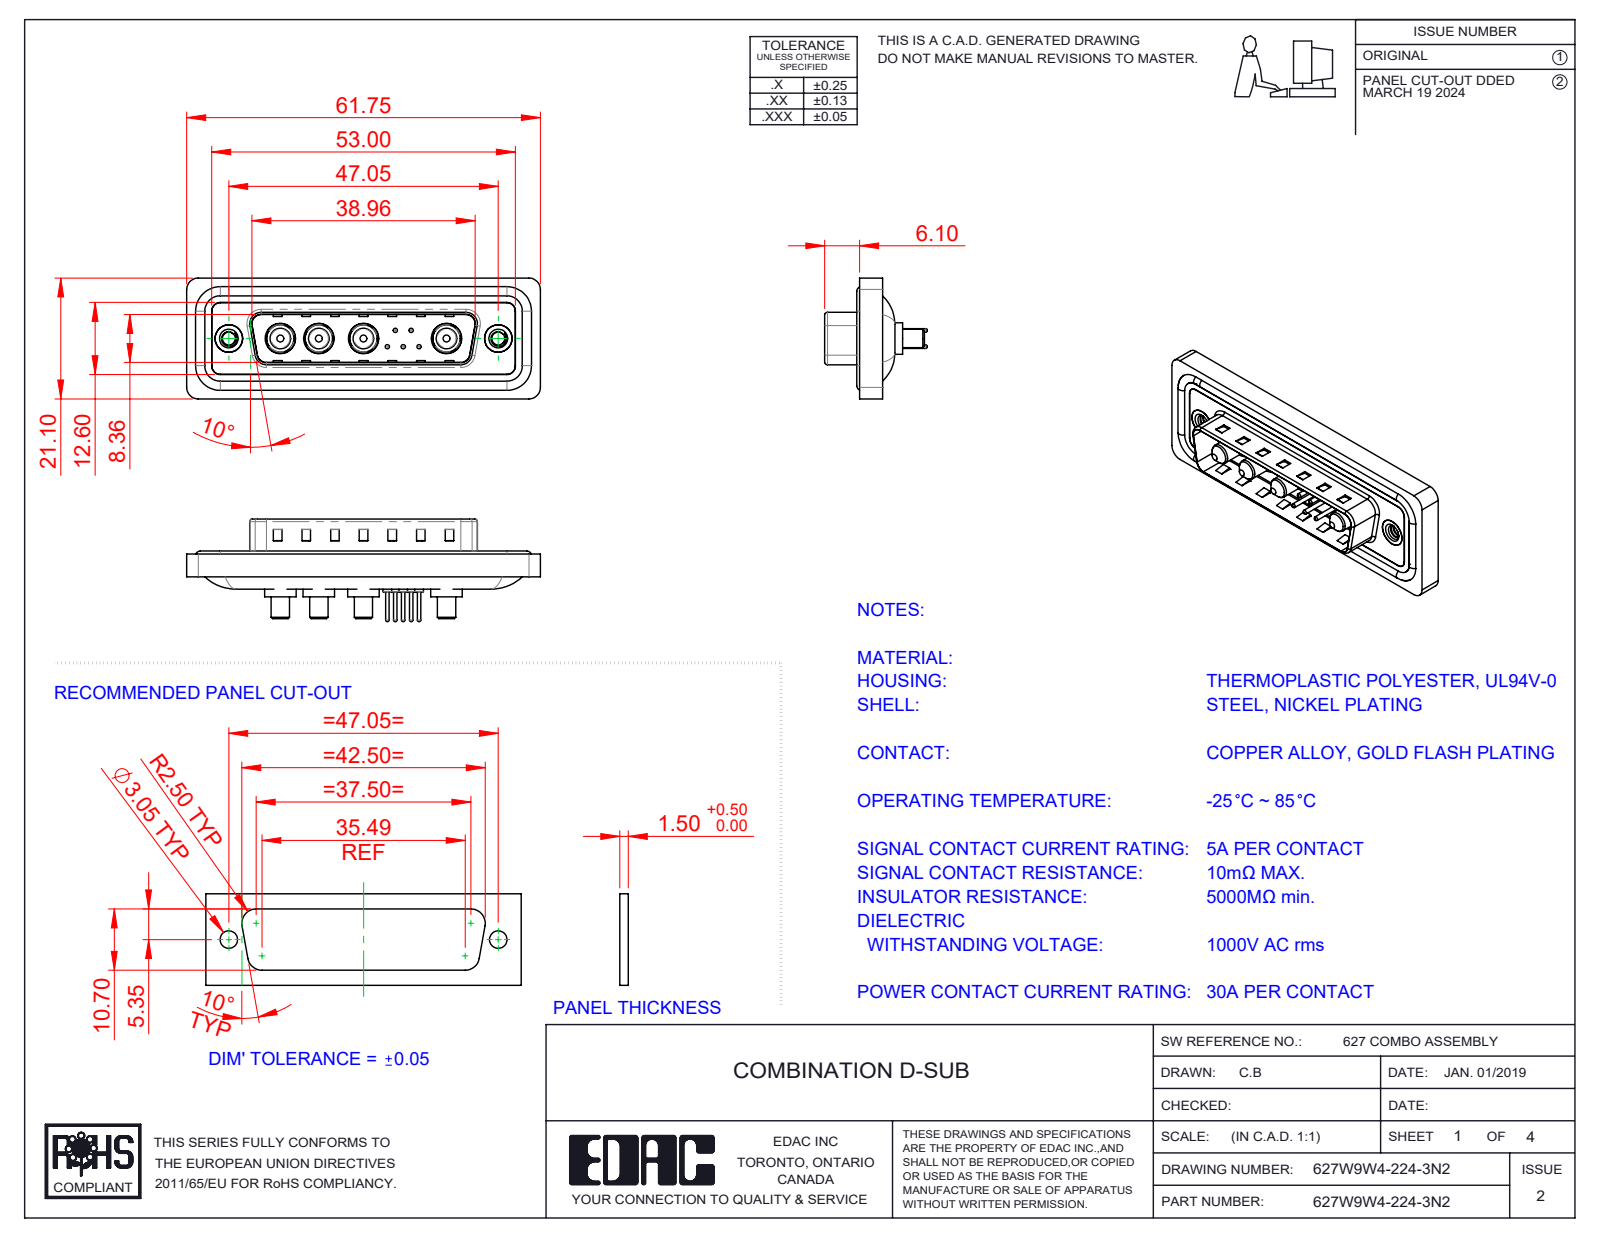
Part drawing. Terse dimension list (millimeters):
name: 627Combo Contact Row 1_24; 627Combo Waterproof Housing_25 Contacts; 627W9W4-224-3N2; 627Combo Shell Rear_25 Contacts (+5 more)
written by: SolidWorks 2023 (CONFIG_CONTROL_DESIGN)
unit: mm
bodies: 20 solids, 824 faces (284 planar, 334 cylindrical, 206 other)
size: 61.75 × 21.1 × 17.9
volume: 7 432 mm³; area: 11 854 mm²
holes: 5× ⌀0.75, 5× ⌀1.6, 5× ⌀2, 4× ⌀4.85, 4× ⌀5.3, 2× ⌀2.26, 2× ⌀4, 2× ⌀4.8, 2× ⌀5
bosses: 5× ⌀1.5, 5× ⌀0.6, 4× ⌀5.5, 4× ⌀5.2, 4× ⌀4.75, 4× ⌀3.75, 4× ⌀3.6, 4× ⌀3.2
rounds: 22× R1.5, 18× R2, 8× R0.5, 8× R1.6, 4× R0.25, 4× R0.6, 4× R0.65, 4× R0.9
face distances: 0.4, 1.5, 1.1, 0.5, 1.6, 3.1, 2.9, 0.82, 9.58, 5.65
hole spacings: 3.16, 2.77, 5.04, 14.51, 2.78, 4.4, 4.41, 5
